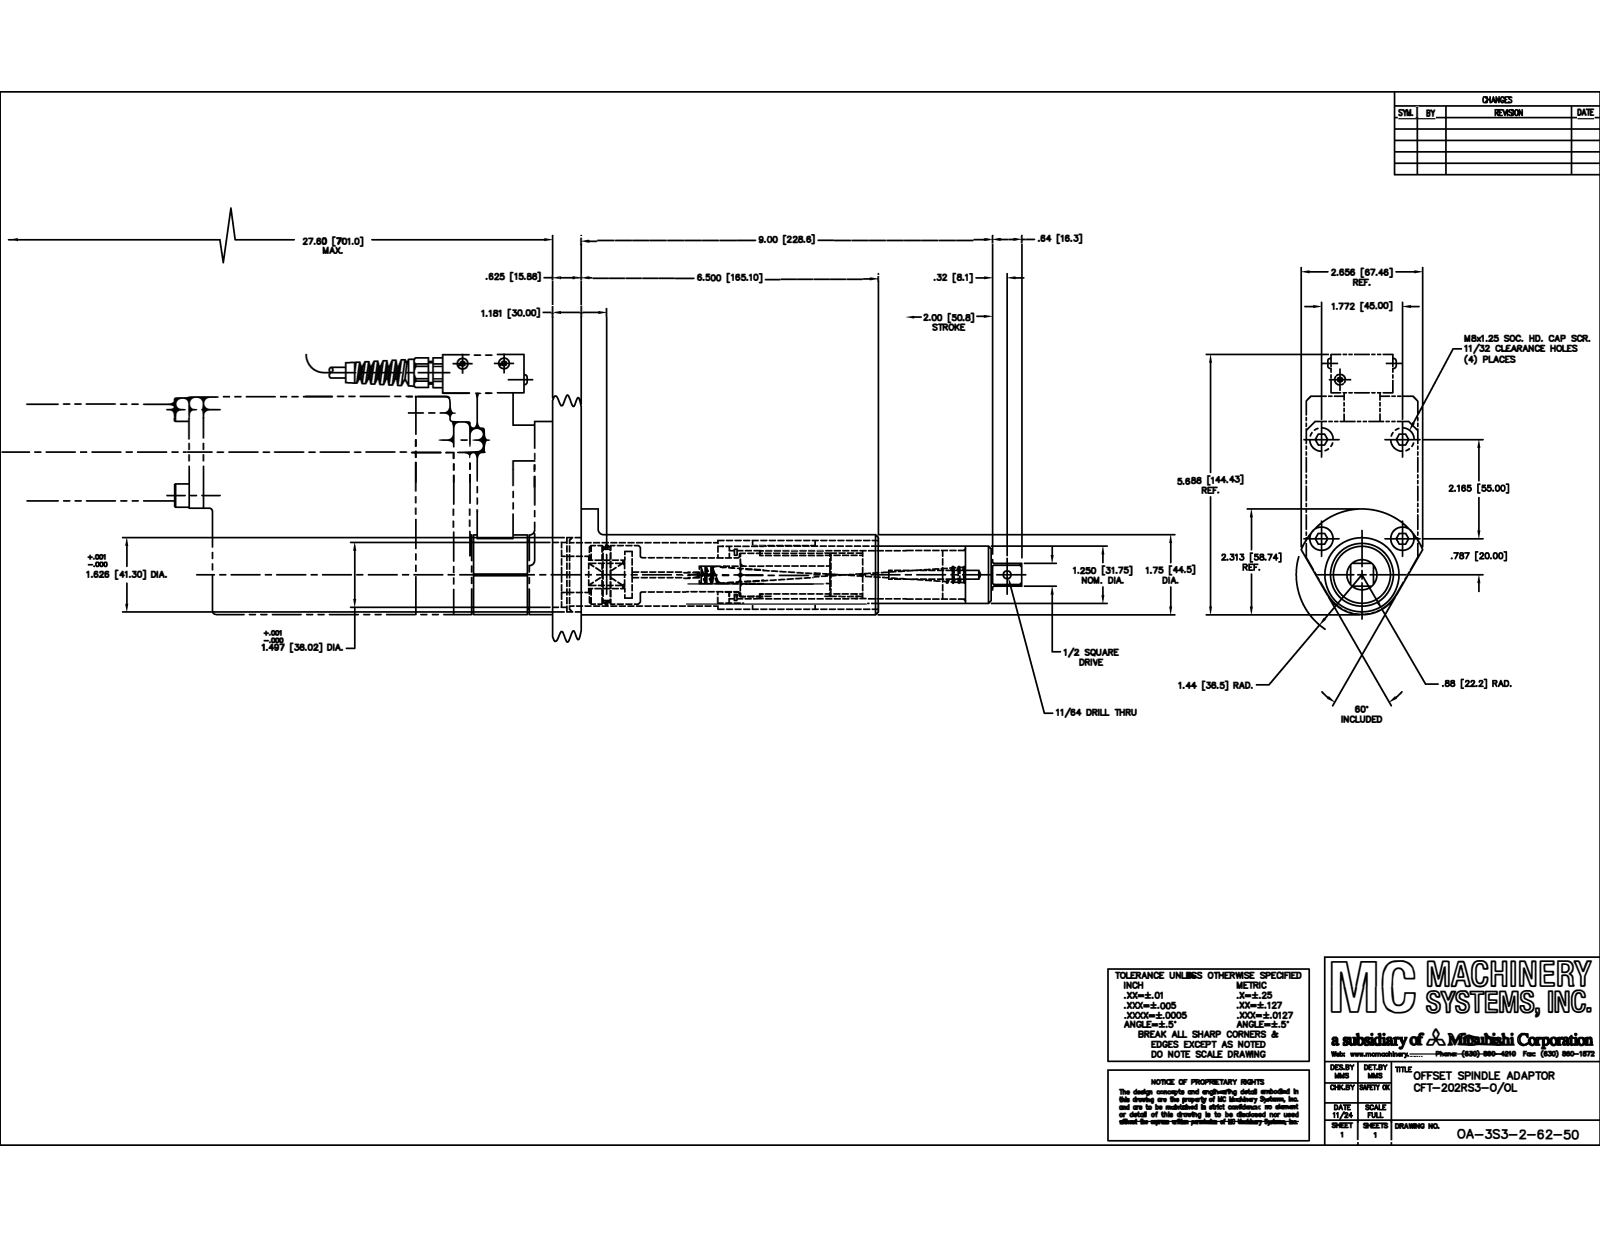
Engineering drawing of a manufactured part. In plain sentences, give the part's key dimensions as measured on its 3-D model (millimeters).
The part is named "SA-158H; J-2016-3; SCE2016; J-2016 (+8 more)". Its 3-D file was written by "SolidWorks 2016 (CONFIG_CONTROL_DESIGN)". It is 13 solids with 253 faces: 72 planar, 120 cylindrical and 61 other. Overall it measures 248 by 59.9 by 58.7 millimeters. Its volume is 213 200 cubic millimeters and its surface area 119 400 square millimeters. Round holes: 2 of diameter 2, 2 of diameter 8.7, 1 of diameter 3.2, 1 of diameter 4.4, 1 of diameter 4.7, 1 of diameter 6.4, 1 of diameter 9.5, 1 of diameter 9.9, 1 of diameter 22.9, 1 of diameter 25.5, 1 of diameter 26.6, 1 of diameter 27. Round bosses or shafts: 4 of diameter 2.2, 1 of diameter 44.5, 1 of diameter 41.3, 1 of diameter 38.1, 1 of diameter 37.6, 1 of diameter 35.2, 1 of diameter 31.8, 1 of diameter 28.6. Partial cylindrical surfaces (rounded edges, fillets, slot ends): 4 of radius 0.8, 4 of radius 1.2, 4 of radius 2.1, 2 of radius 2, 1 of radius 9.6, 1 of radius 10.6, 1 of radius 36.5. The main face-to-face distances are 9.5, 25.4, 60.3, 1.7, 14.2, 59.9, 210.4, 200.9, 36.2, 165.1. The hole center spacings are 9.4, 30.1, 9.1, 20.9, 22.3, 28, 31, 45.
